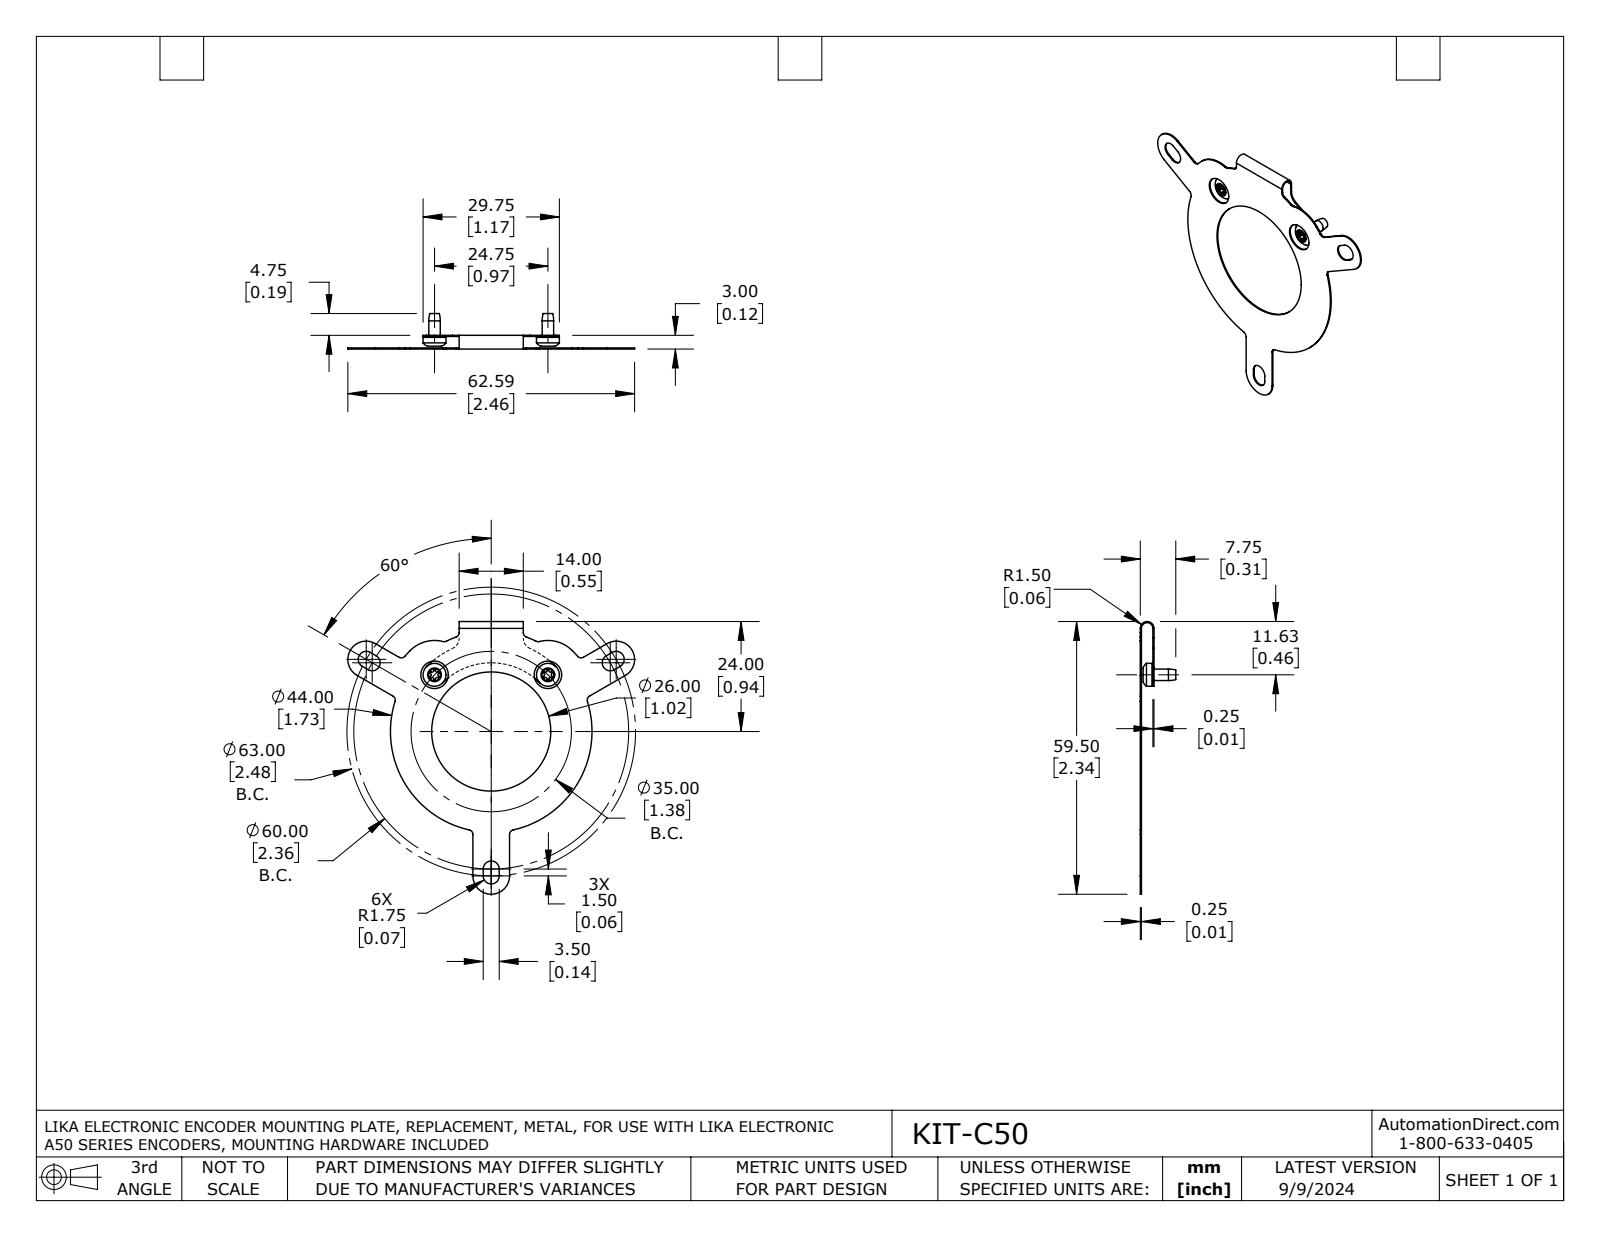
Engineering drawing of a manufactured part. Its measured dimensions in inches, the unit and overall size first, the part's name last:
Units: inches
Overall size (bounding box): 2.464 × 2.343 × 0.305
Round holes (diameter × count): ⌀0.11 ×2, ⌀0.236 ×2, ⌀1.024 ×1
Round bosses / shafts (diameter × count): ⌀0.197 ×2, ⌀0.098 ×2
Partial cylindrical surfaces — rounded edges, fillets, slot ends (radius × count): R0.007 ×12, R0.015 ×12, R0.039 ×10, R0.069 ×6, R0.157 ×3, R0.098 ×2, R0.295 ×2, R0.049 ×1
Main face-to-face distances: 0.108, 0.098, 0.118, 0.187, 0.197, 0.295, 0.305, 0.241, 0.054, 0.044
Hole centre spacings: 0.689, 0.974
Volume: 0.03 in³ · Surface area: 5.152 in²
Bodies: 3 solids, 144 faces (26 planar, 102 cylindrical, 16 other)
Part name (STEP PRODUCT): KIT-C50
STEP written by: SolidWorks 2021 (AUTOMOTIVE_DESIGN)
